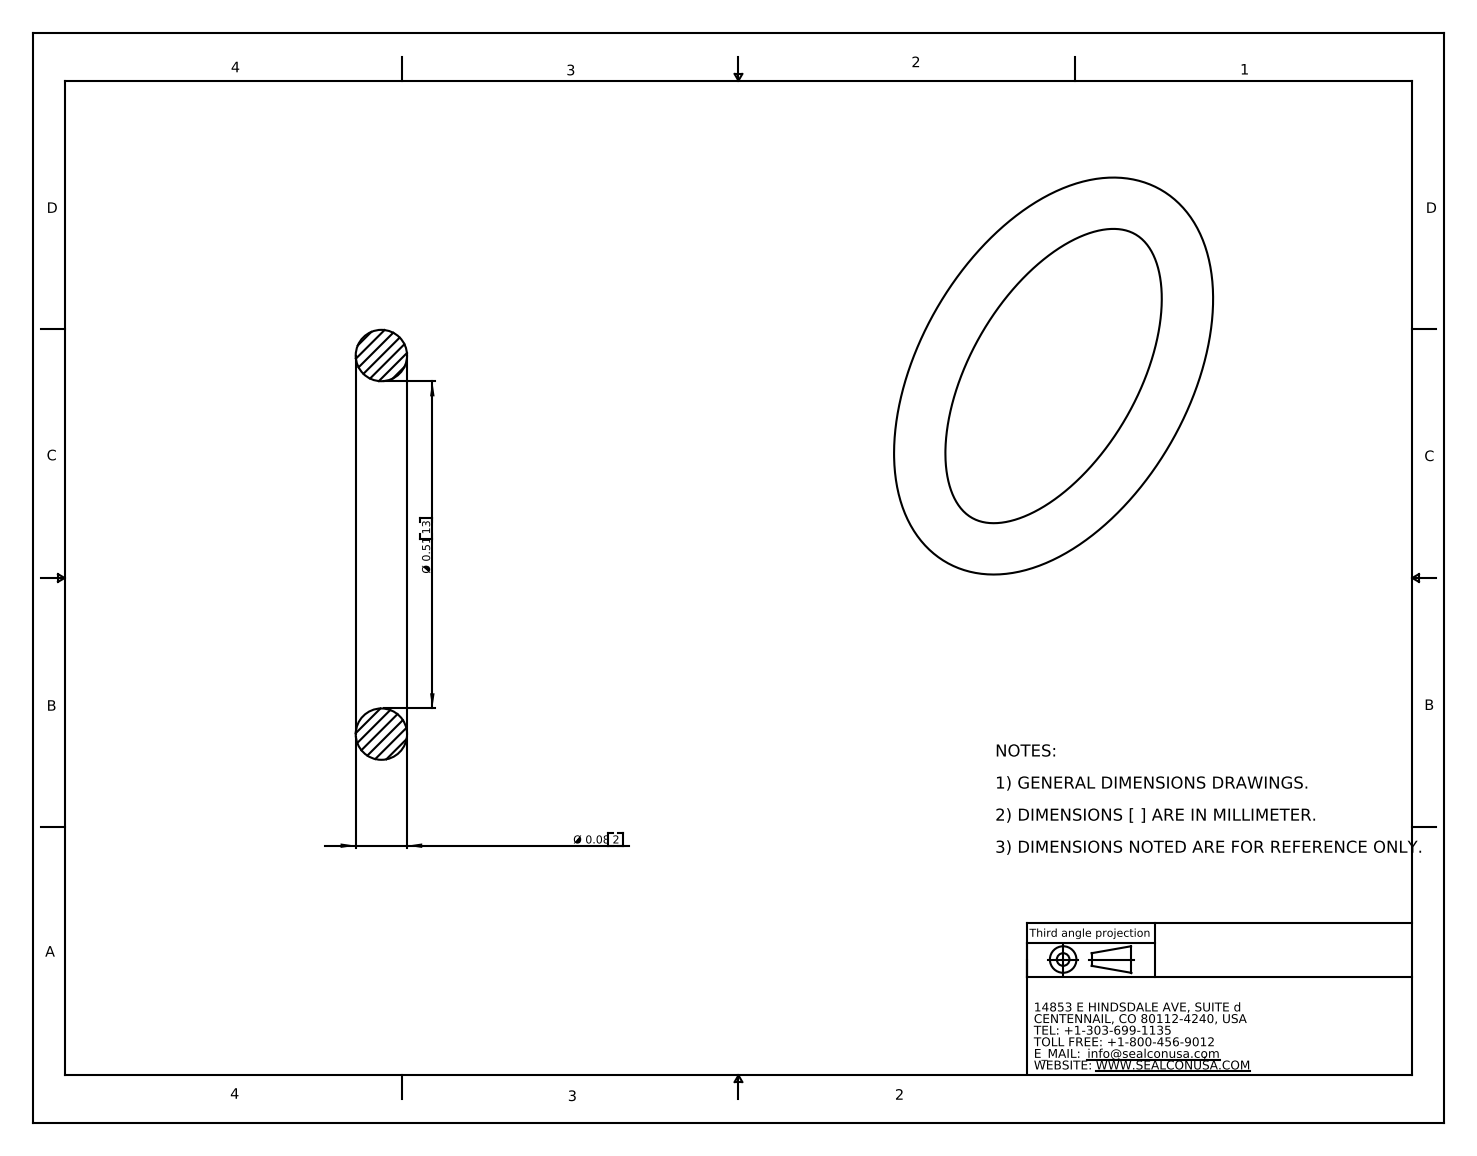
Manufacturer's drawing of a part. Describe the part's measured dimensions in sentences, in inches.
The part is named "OR-38-BN". Its 3-D file was written by "SolidWorks 2007 (CONFIG_CONTROL_DESIGN)". It is 1 solid with 4 faces: 0 planar, 0 cylindrical and 4 other. Overall it measures 0.67 by 0.67 by 0.08 inches. Its volume is 0.009 cubic inches and its surface area 0.466 square inches.
